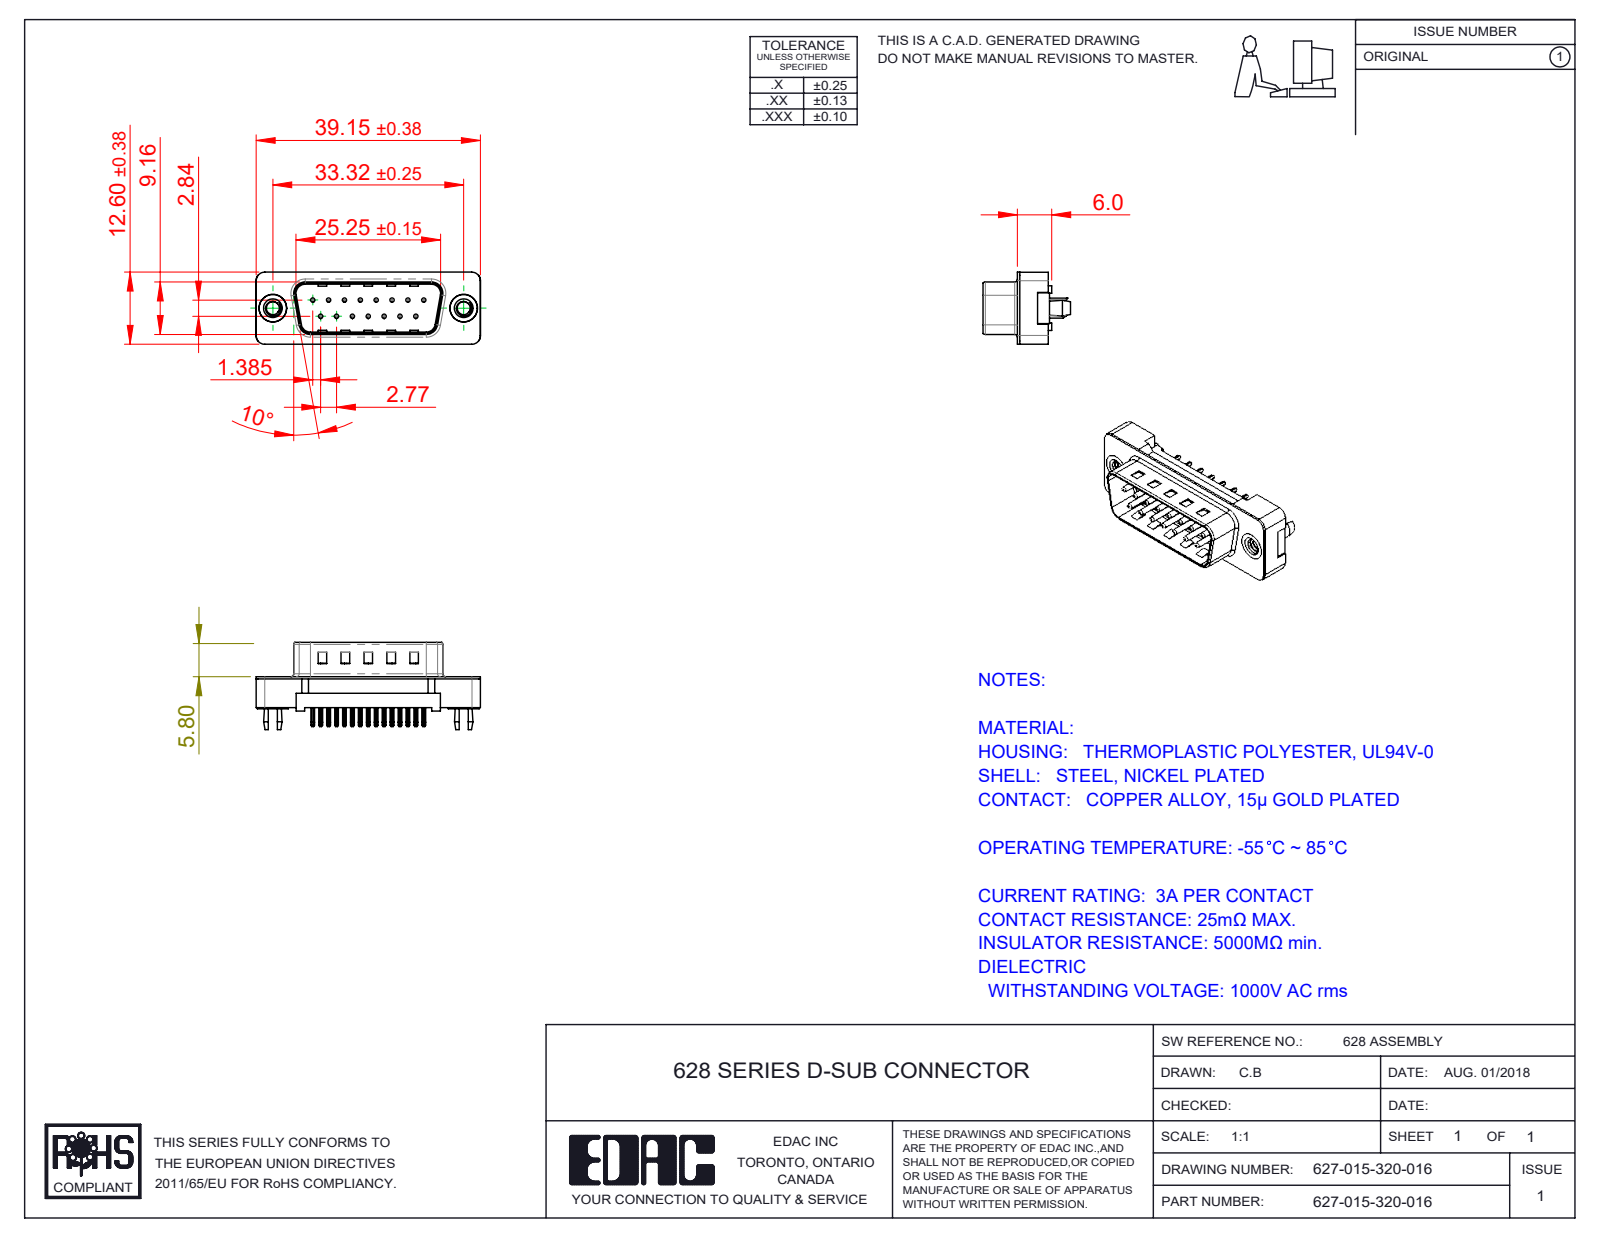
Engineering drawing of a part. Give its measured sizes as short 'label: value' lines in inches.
name: 627 PB 4-40 Threaded Rivet with Boardlock; 627-015-320-016; 627 PB Contact Row 1_20; 627 Plastic Body Housing_15 Contacts (+2 more)
written by: SolidWorks 2020 (CONFIG_CONTROL_DESIGN)
unit: in
bodies: 19 solids, 1177 faces (751 planar, 334 cylindrical, 92 other)
size: 1.543 × 0.6 × 0.496
volume: 0.123 in³; area: 6.744 in²
holes: 15× ⌀0.014, 15× ⌀0.033, 2× ⌀0.089, 2× ⌀0.157, 2× ⌀0.189, 2× ⌀0.197
bosses: 15× ⌀0.03, 2× ⌀0.193
rounds: 30× R0.01, 15× R0.005, 8× R0.02, 8× R0.059, 4× R0.035, 4× R0.063, 4× R0.079, 2× R0.016
face distances: 0.016, 0.098, 0.213, 0.345, 0.197, 0.114, 0.355, 0.334, 0.062, 0.027
hole spacings: 0.124, 0.109, 0.218, 0.327, 0.198, 0.294, 0.436, 0.198
